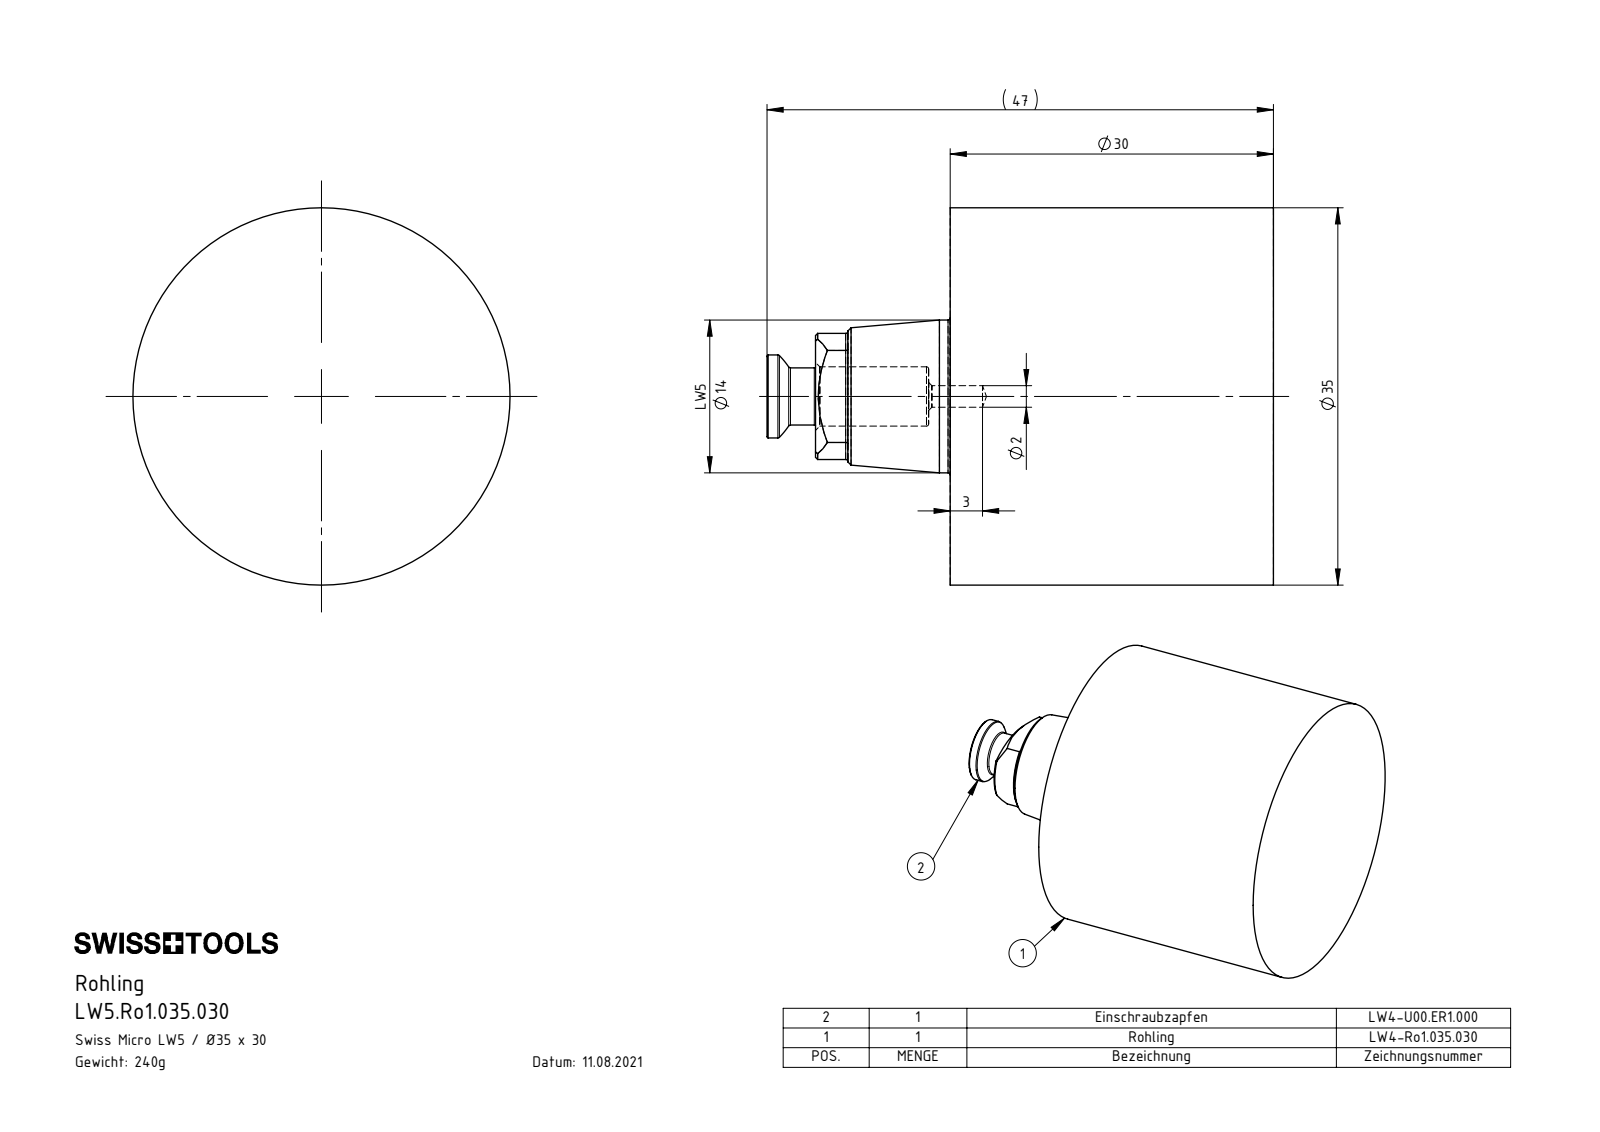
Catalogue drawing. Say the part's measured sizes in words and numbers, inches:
The part is named "LW4-Ro1.035.030_A; LW4-U00.ER1.000_B; LW4.Ro1.035.030". Its 3-D file was written by "SolidWorks 2017 (AUTOMOTIVE_DESIGN)". It is 2 solids with 53 faces: 15 planar, 13 cylindrical and 25 other. Overall it measures 1.85 by 1.378 by 1.378 inches. Its volume is 1.864 cubic inches and its surface area 9.833 square inches. Round holes: 1 of diameter 0.079, 1 of diameter 0.098, 1 of diameter 0.217. Round bosses or shafts: 1 of diameter 1.378, 1 of diameter 0.558, 1 of diameter 0.303, 1 of diameter 0.236, 1 of diameter 0.209, 1 of diameter 0.197. Partial cylindrical surfaces (rounded edges, fillets, slot ends): 2 of radius 0.008, 1 of radius 0.23. The main face-to-face distances are 1.181, 0.295, 0.079, 0.492, 1.673, 0.177, 0.669, 1.85, 0.591, 0.413.
